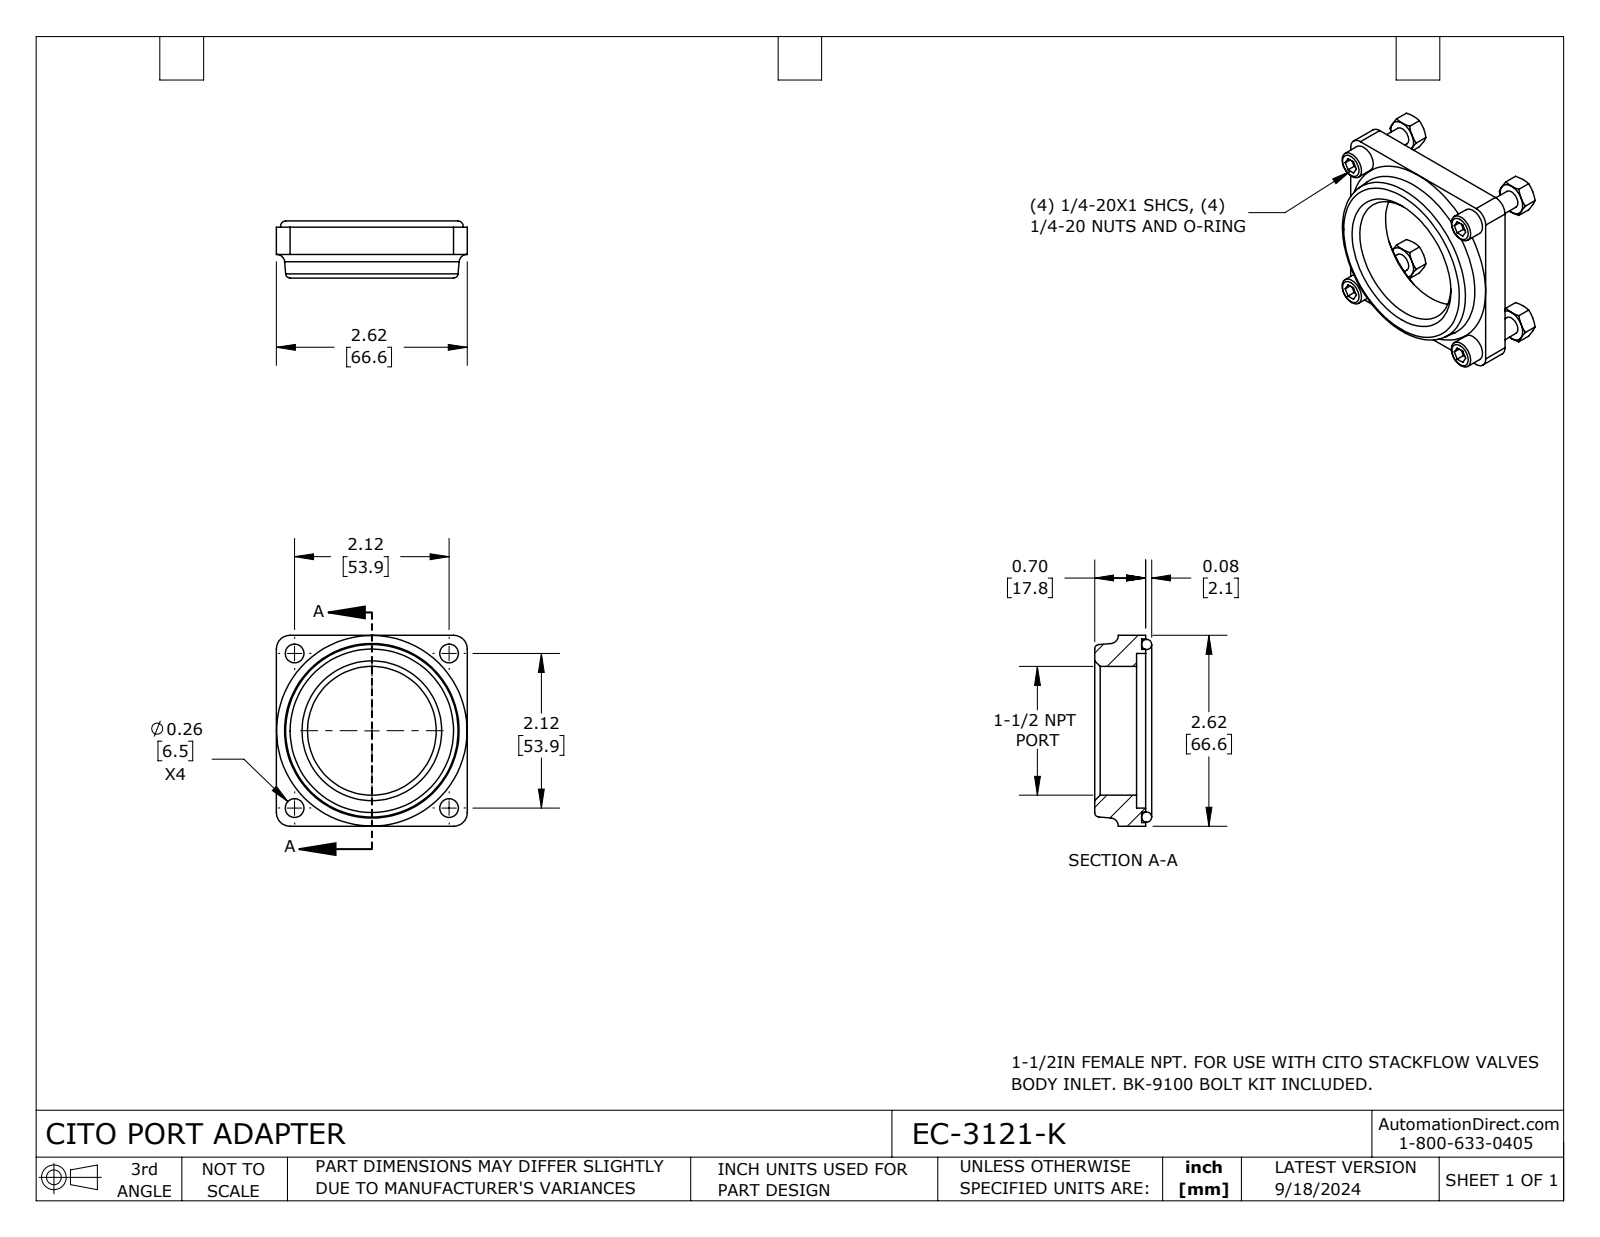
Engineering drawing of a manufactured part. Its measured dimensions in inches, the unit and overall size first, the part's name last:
Units: inches
Overall size (bounding box): 2.624 × 2.624 × 0.784
Round holes (diameter × count): ⌀0.257 ×4, ⌀1.77 ×1, ⌀2.125 ×1, ⌀2.525 ×1
Round bosses / shafts (diameter × count): ⌀2.234 ×1
Partial cylindrical surfaces — rounded edges, fillets, slot ends (radius × count): R0.187 ×2, R0.188 ×2
Main face-to-face distances: 2.624, 0.375, 0.32, 0.055, 0.25, 0.07, 0.125, 0.325, 0.575, 0.645
Hole centre spacings: 1.502, 2.124, 3.003
Volume: 2.139 in³ · Surface area: 23.06 in²
Bodies: 2 solids, 42 faces (10 planar, 20 cylindrical, 12 other)
Part name (STEP PRODUCT): EC-3121-K
STEP written by: SolidWorks 2023 (CONFIG_CONTROL_DESIGN)
